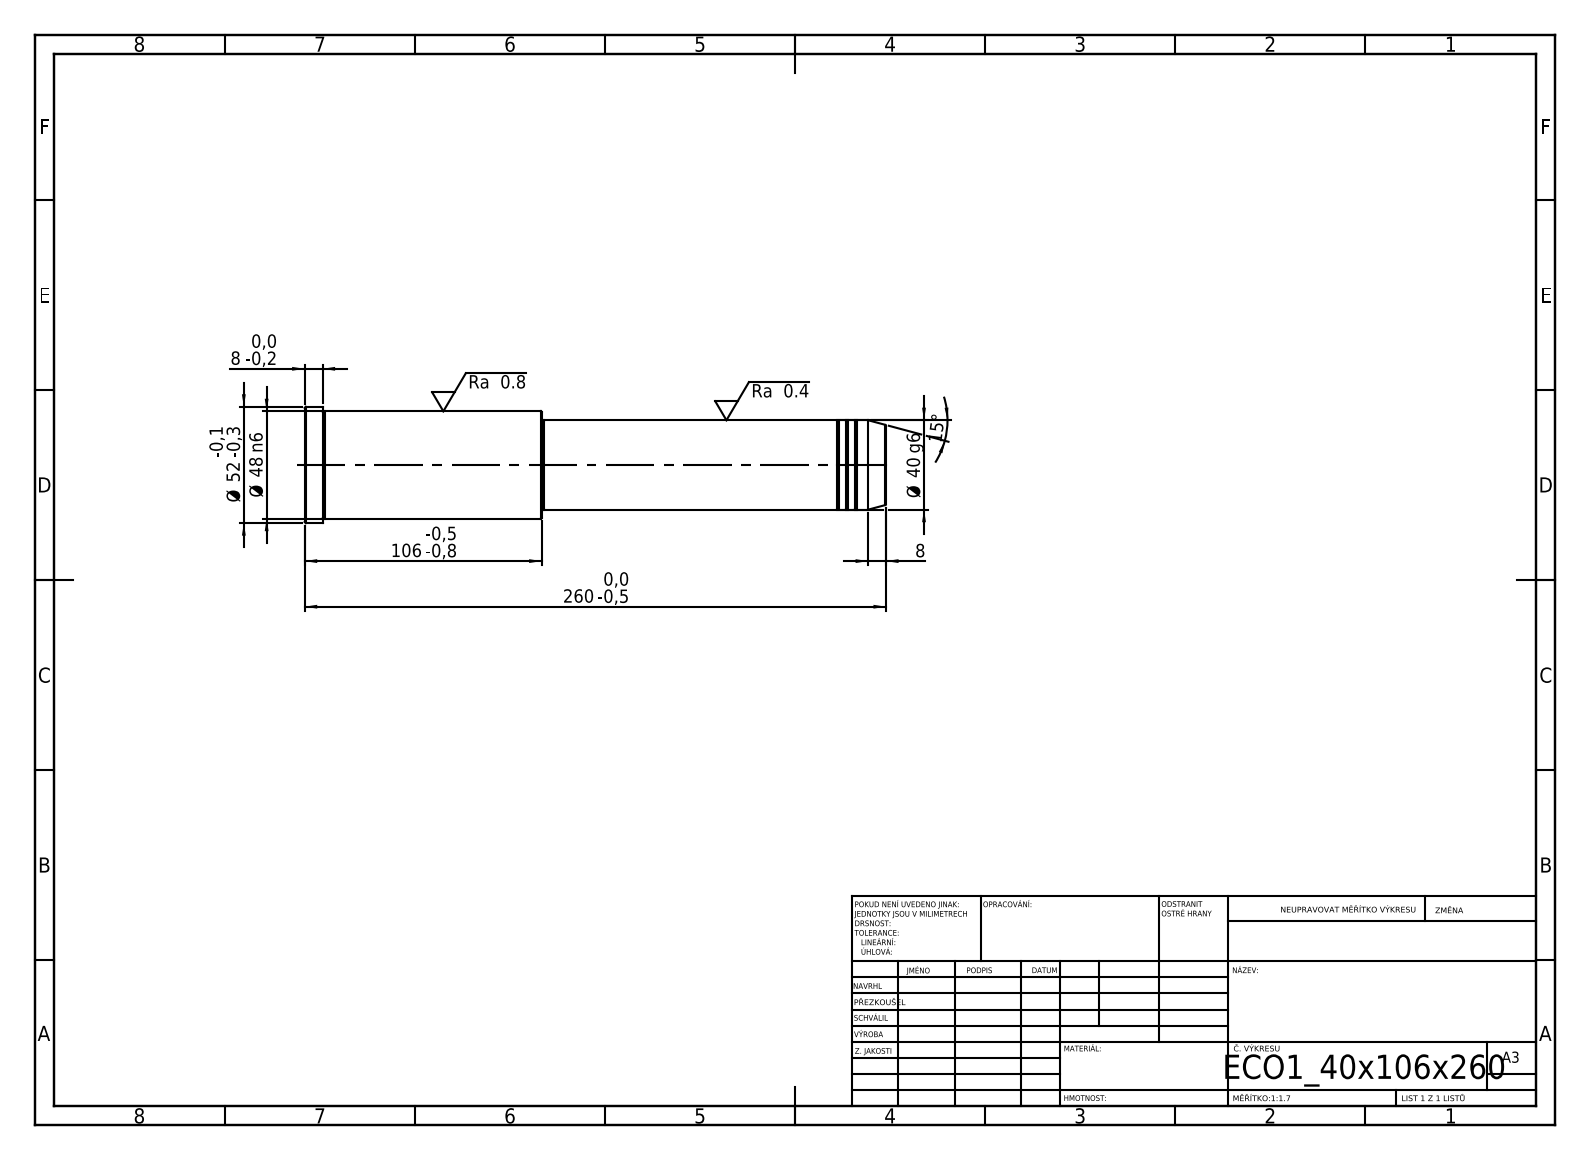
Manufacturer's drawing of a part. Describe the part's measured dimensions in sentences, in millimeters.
Its 3-D file was written by "SolidWorks 2019 (CONFIG_CONTROL_DESIGN)". It is 1 solid with 43 faces: 5 planar, 14 cylindrical and 24 other. Overall it measures 260 by 52 by 52 millimeters. Its volume is 386 500 cubic millimeters and its surface area 39 714 square millimeters. Round bosses or shafts: 1 of diameter 52, 1 of diameter 48, 1 of diameter 40, 1 of diameter 39. The main face-to-face distances are 260, 154, 106, 252, 98, 8, 153, 1, 99, 107.
